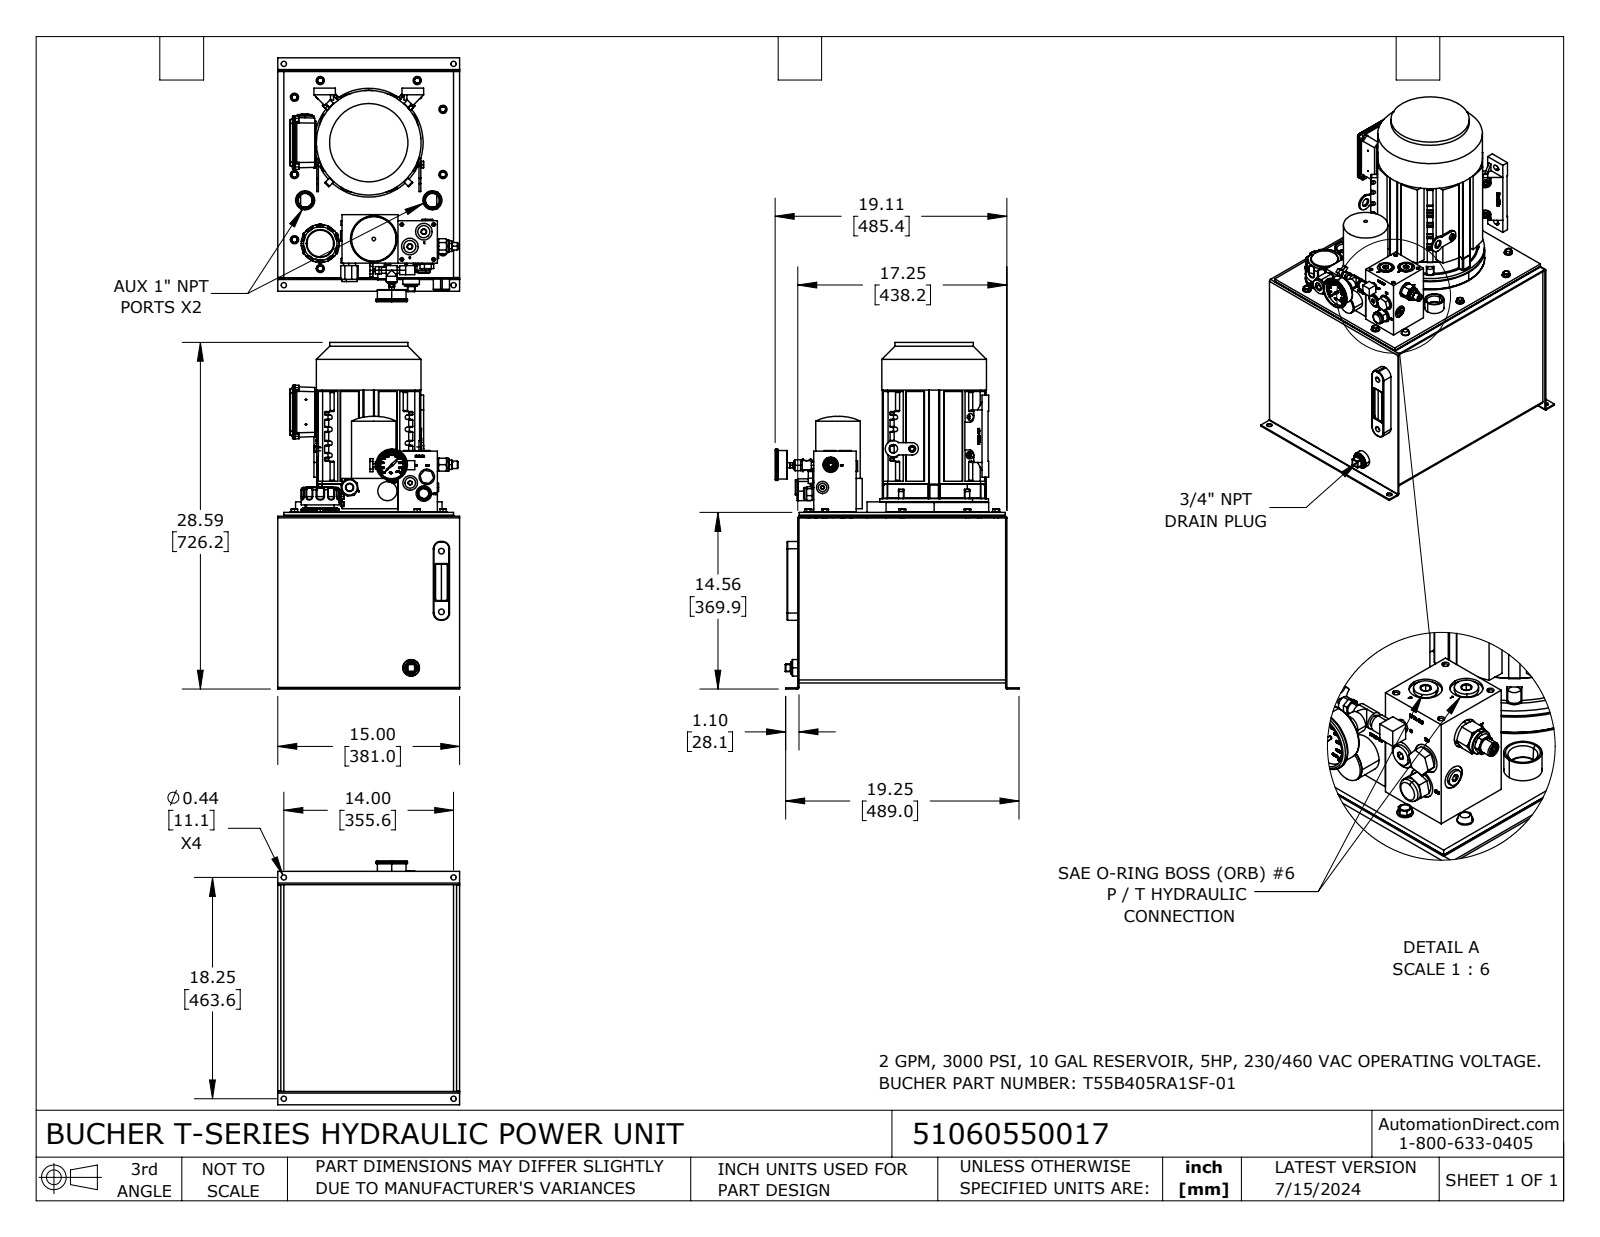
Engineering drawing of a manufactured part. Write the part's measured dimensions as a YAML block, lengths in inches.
part_name: "51060550017"
step_written_by: "SolidWorks 2023 (CONFIG_CONTROL_DESIGN)"
units: inches
bodies: {solids: 68, faces: 5194, planar: 2601, cylindrical: 1296, other: 1297}
overall_size: [28.589, 20.112, 15]
volume: 1146
surface_area: 4922
round_holes:
  - {diameter: 0.437, count: 17}
  - {diameter: 0.5, count: 11}
  - {diameter: 0.563, count: 10}
  - {diameter: 0.201, count: 8}
  - {diameter: 0.19, count: 6}
  - {diameter: 0.472, count: 6}
  - {diameter: 0.531, count: 6}
  - {diameter: 0.236, count: 5}
  - {diameter: 0.75, count: 5}
  - {diameter: 0.807, count: 5}
  - {diameter: 1.37, count: 5}
  - {diameter: 0.12, count: 4}
round_bosses_or_shafts:
  - {diameter: 0.676, count: 10}
  - {diameter: 0.313, count: 10}
  - {diameter: 0.551, count: 6}
  - {diameter: 0.373, count: 6}
  - {diameter: 0.315, count: 6}
  - {diameter: 0.25, count: 5}
  - {diameter: 0.37, count: 4}
  - {diameter: 1, count: 3}
partial_cylinders:
  - {radius: 0.079, count: 76}
  - {radius: 0.02, count: 68}
  - {radius: 0.039, count: 60}
  - {radius: 0.063, count: 21}
  - {radius: 0.167, count: 20}
  - {radius: 0.118, count: 16}
  - {radius: 0.375, count: 15}
  - {radius: 0.05, count: 13}
face_to_face_distances: [0.104, 0.105, 14.395, 17.145, 0.25, 0.313, 13.635, 13.802, 14.5, 0.063]
hole_center_spacings: [3.469, 1.442, 2.497, 1.441, 0.78, 2.874, 3.3, 3.976]
